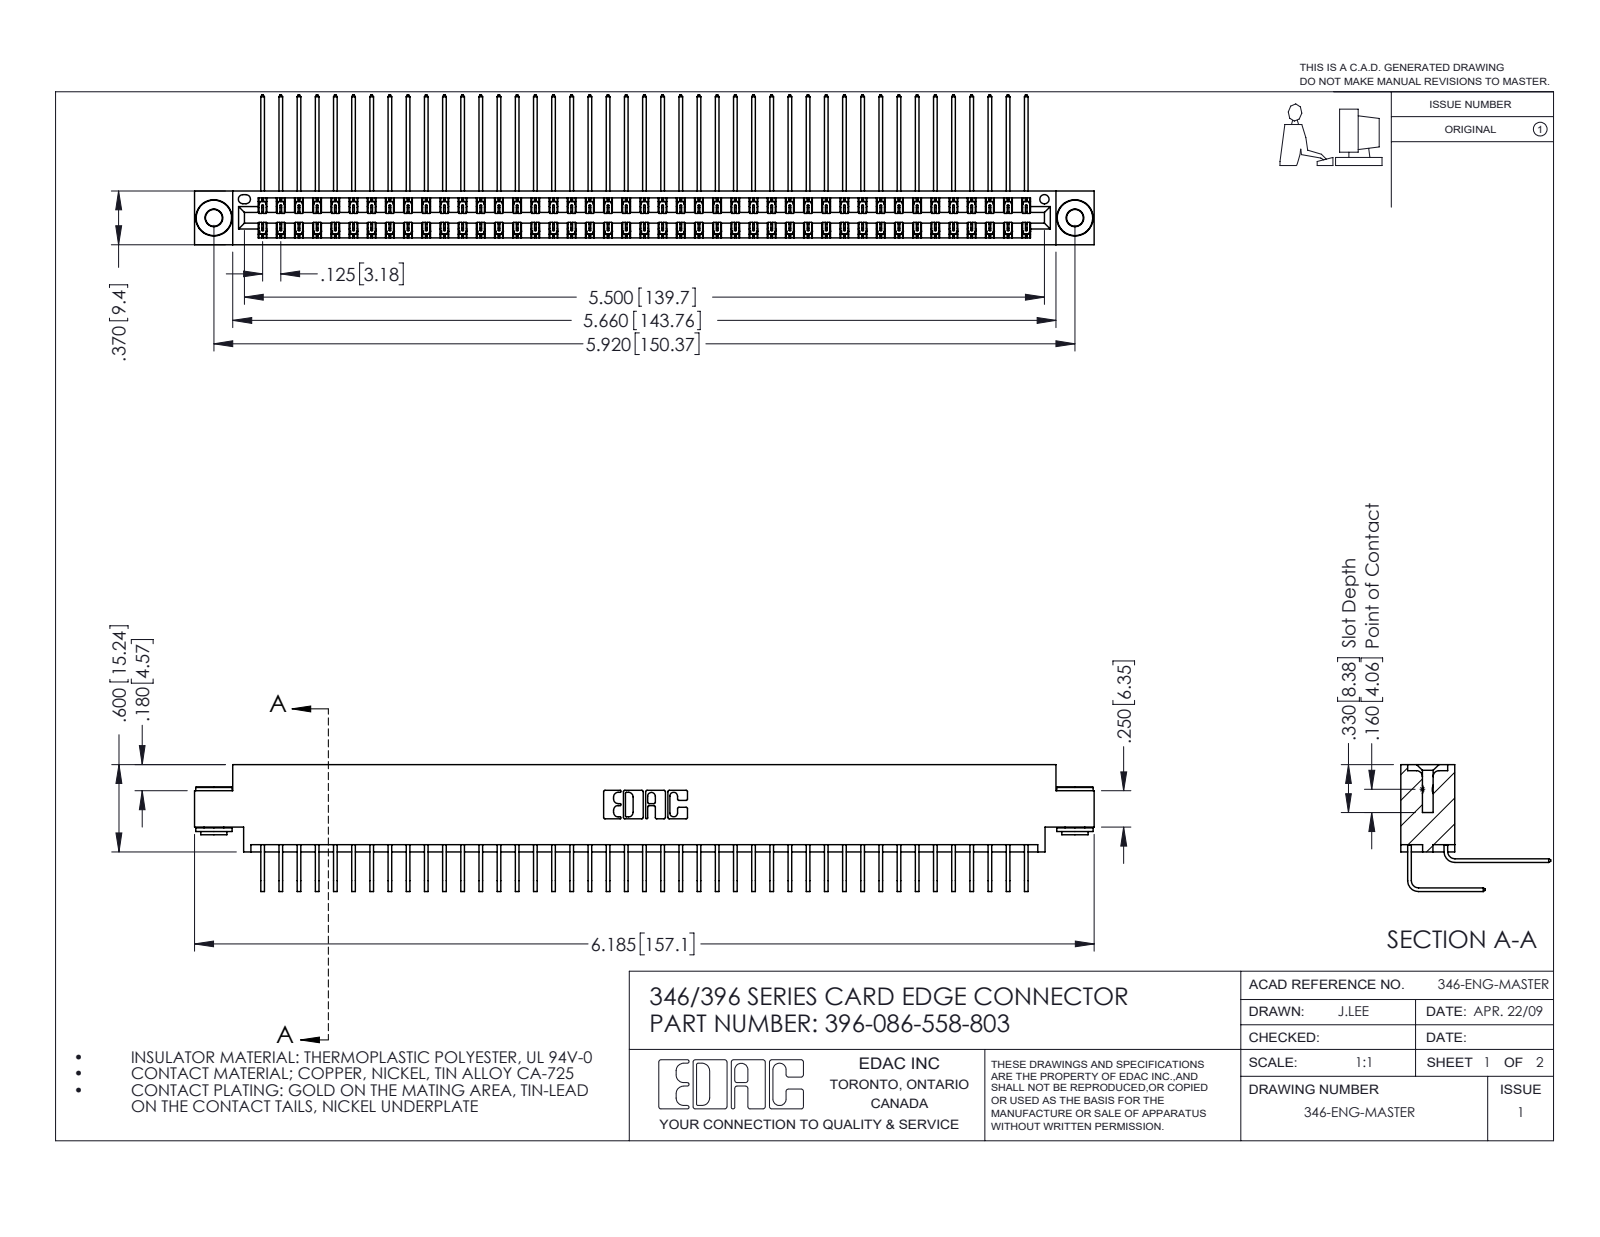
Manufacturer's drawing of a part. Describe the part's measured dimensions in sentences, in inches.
The part is named "345-292-001_558 559 Tail - 1; 396-086-558-803; 345-250-002_345-250-002-102; 346 Part_0.170 Offset - 0.156 Dia-TH (+1 more)". Its 3-D file was written by "SolidWorks 2016 (CONFIG_CONTROL_DESIGN)". It is 89 solids with 4808 faces: 3272 planar, 1528 cylindrical and 8 other. Overall it measures 6.185 by 1.03 by 0.873 inches. Its volume is 0.957 cubic inches and its surface area 37.75 square inches. Round holes: 2 of diameter 0.116, 2 of diameter 0.156, 1 of diameter 0.064. Round bosses or shafts: 2 of diameter 0.25, 2 of diameter 0.18, 2 of diameter 0.136. Partial cylindrical surfaces (rounded edges, fillets, slot ends): 129 of radius 0.006, 22 of radius 0.01, 6 of radius 0.007, 6 of radius 0.031, 3 of radius 0.026, 2 of radius 0.014, 2 of radius 0.022, 2 of radius 0.024. The main face-to-face distances are 0.322, 0.048, 0.025, 0.37, 0.25, 0.298, 0.072, 0.275, 0.148, 0.222. The hole center spacings are 0.246, 5.711, 5.92.
